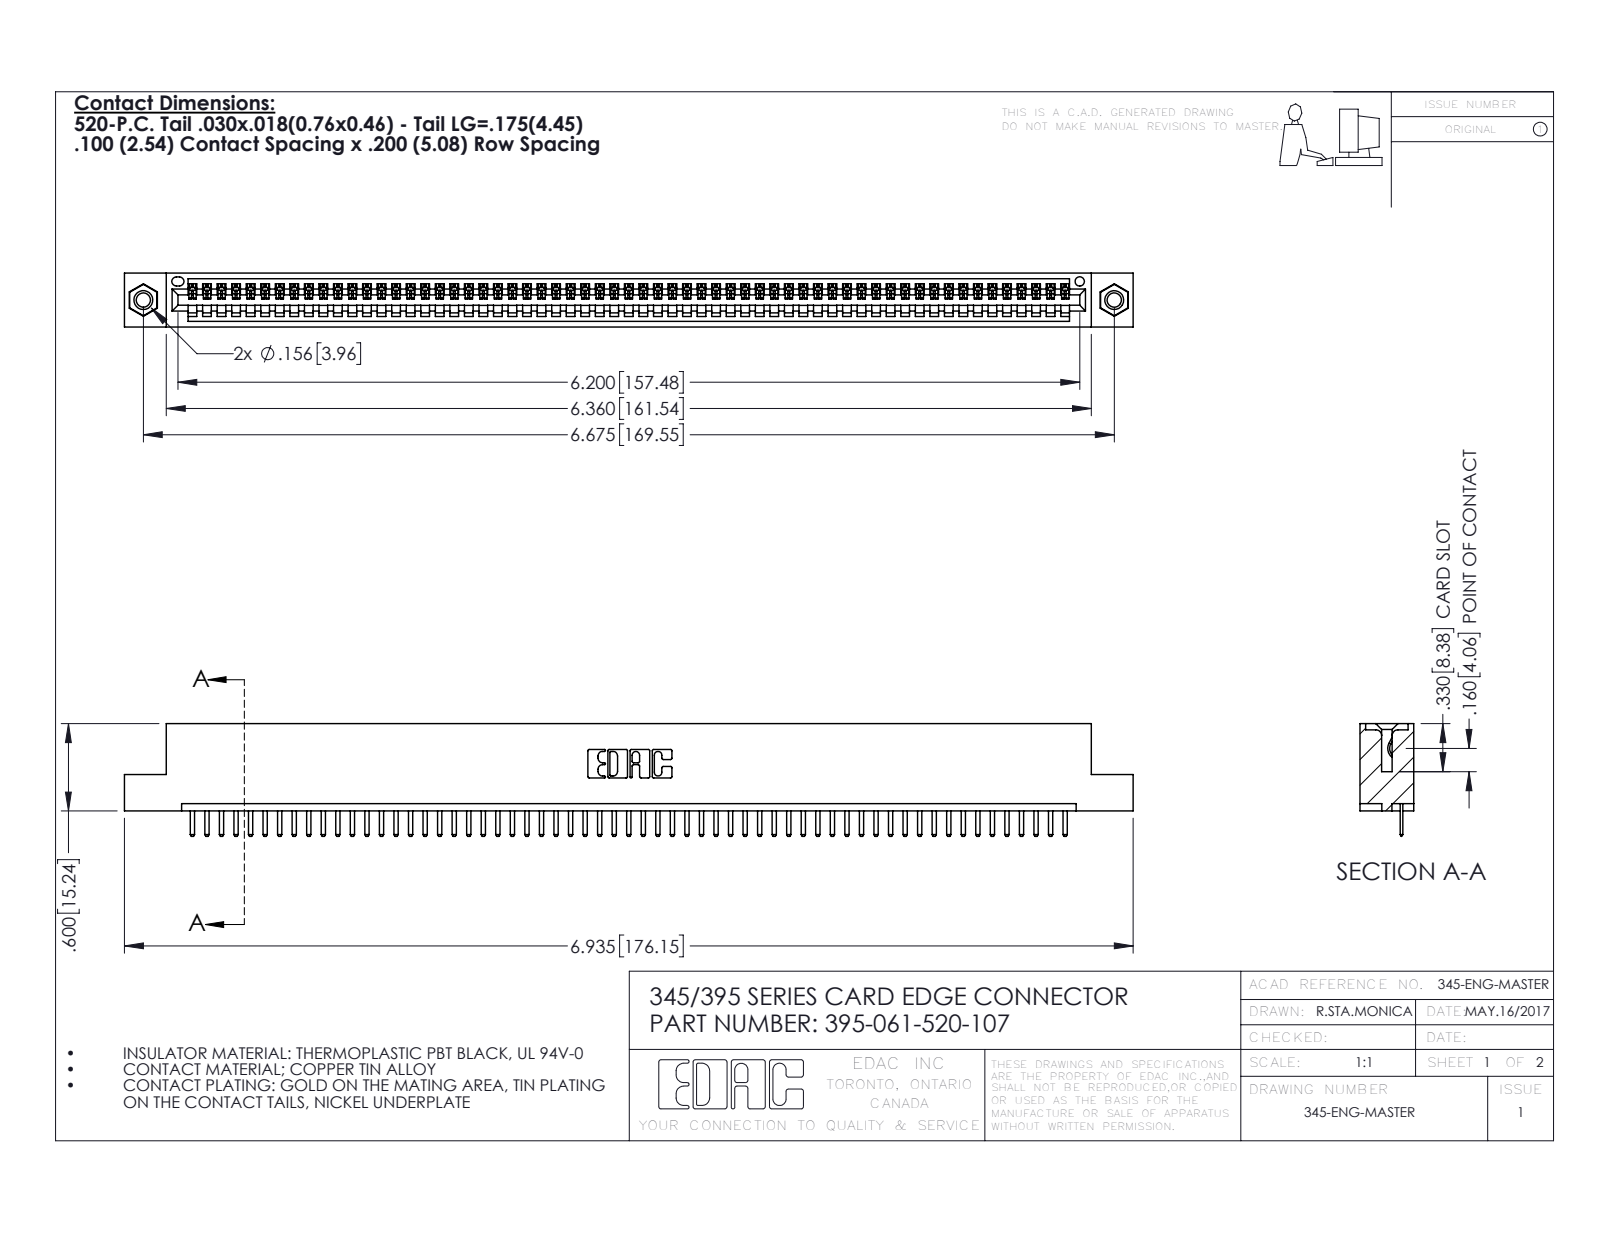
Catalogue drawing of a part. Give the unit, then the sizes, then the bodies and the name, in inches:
Units: inches
Overall size (bounding box): 6.935 × 0.775 × 0.37
Round holes (diameter × count): ⌀0.098 ×2, ⌀0.125 ×2, ⌀0.156 ×2, ⌀0.064 ×1
Round bosses / shafts (diameter × count): ⌀0.155 ×2
Partial cylindrical surfaces — rounded edges, fillets, slot ends (radius × count): R0.01 ×124, R0.006 ×122, R0.01 ×22, R0.007 ×6, R0.031 ×6, R0.026 ×3, R0.031 ×2, R0.04 ×2
Main face-to-face distances: 0.072, 0.298, 0.37, 0.2, 0.098, 0.272, 0.025, 0.225, 0.072, 0.149
Hole centre spacings: 0.27, 6.439, 6.675
Volume: 1.019 in³ · Surface area: 33.95 in²
Bodies: 64 solids, 3968 faces (2674 planar, 1278 cylindrical, 16 other)
Part name (STEP PRODUCT): 345 Part_Flush Mounting Lugs - 0.156 Dia-TI; 395-061-520-107; 345-250-001_345-250-005-103; 345-292-001_345-293-120
STEP written by: SolidWorks 2016 (CONFIG_CONTROL_DESIGN)
